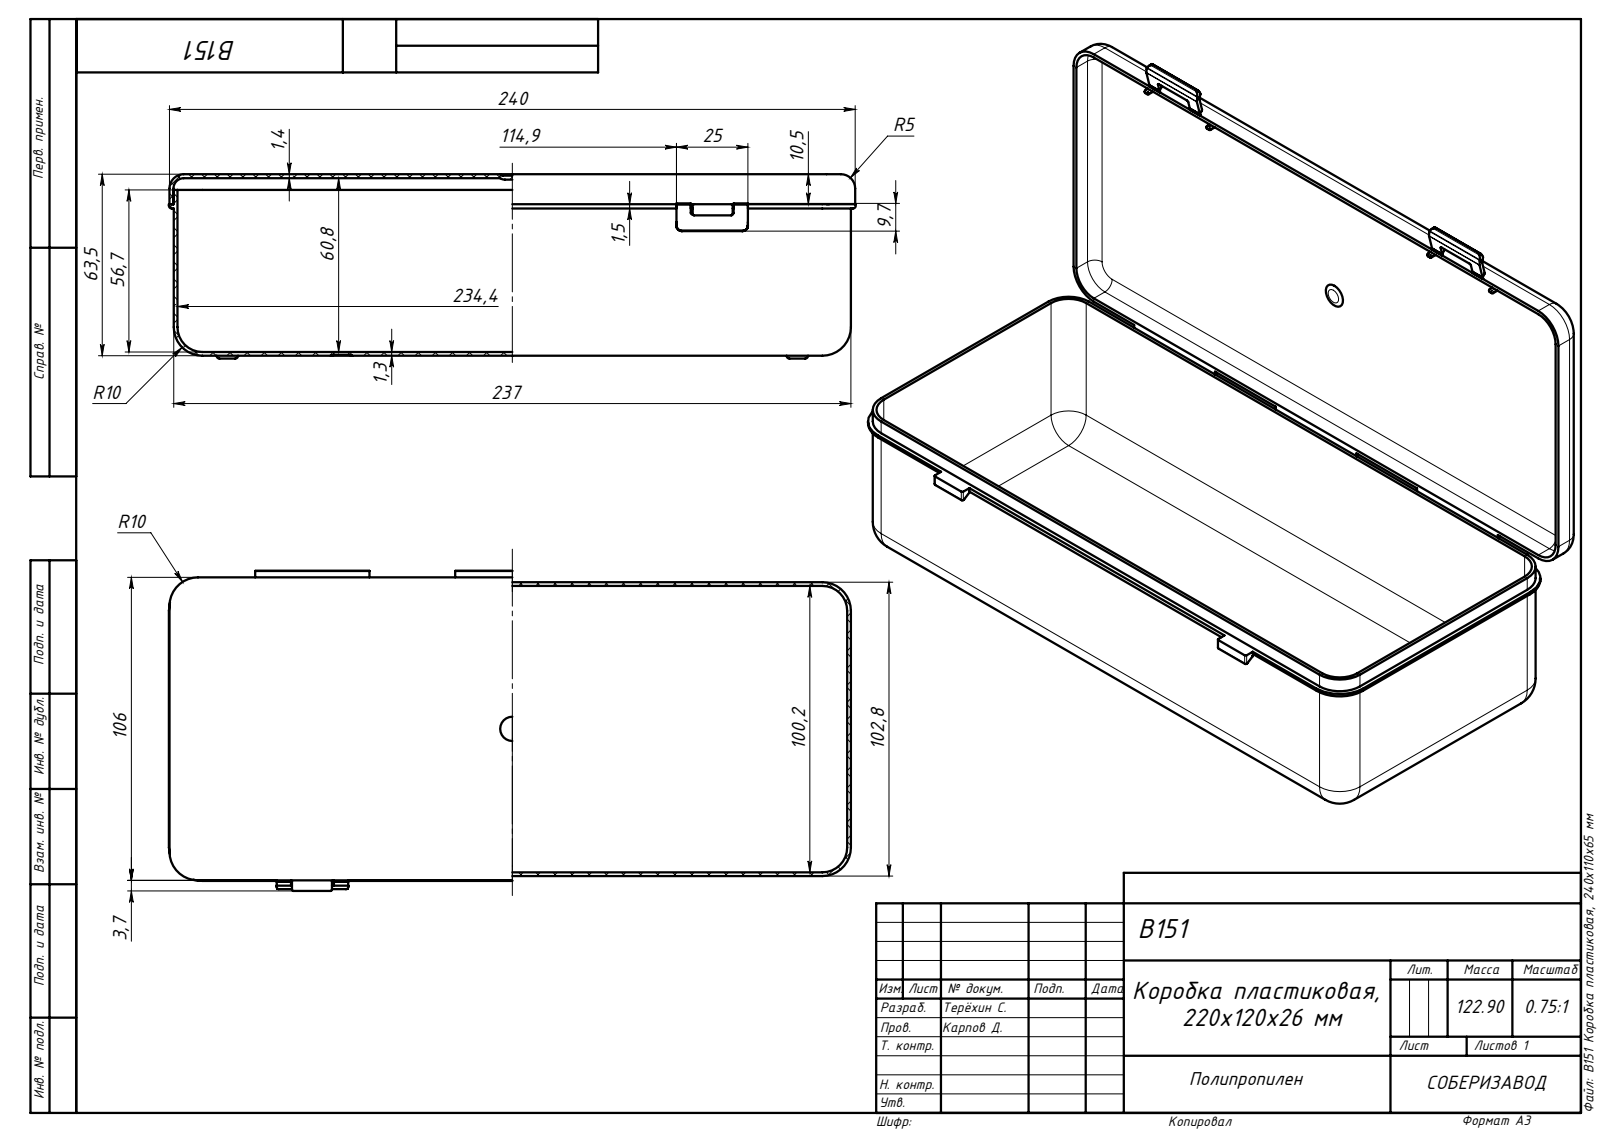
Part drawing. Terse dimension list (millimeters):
name: B151 Крышка_12; B151 Емкость_00; B151 Защёлка_00; B151 Коробка пластиковая, 240x110x65 мм
written by: SolidWorks 2019 (AUTOMOTIVE_DESIGN)
unit: mm
bodies: 10 solids, 328 faces (143 planar, 121 cylindrical, 64 other)
size: 240.4 × 111.95 × 64.5
volume: 121 873 mm³; area: 184 888 mm²
rounds: 53× R0.5, 12× R10, 8× R8.7, 4× R1, 4× R2, 4× R3.6, 4× R5, 4× R8.6
face distances: 1.3, 1.4, 101.5, 60.8, 62.2, 63.5, 62.1, 100.2, 102.8, 235.7
